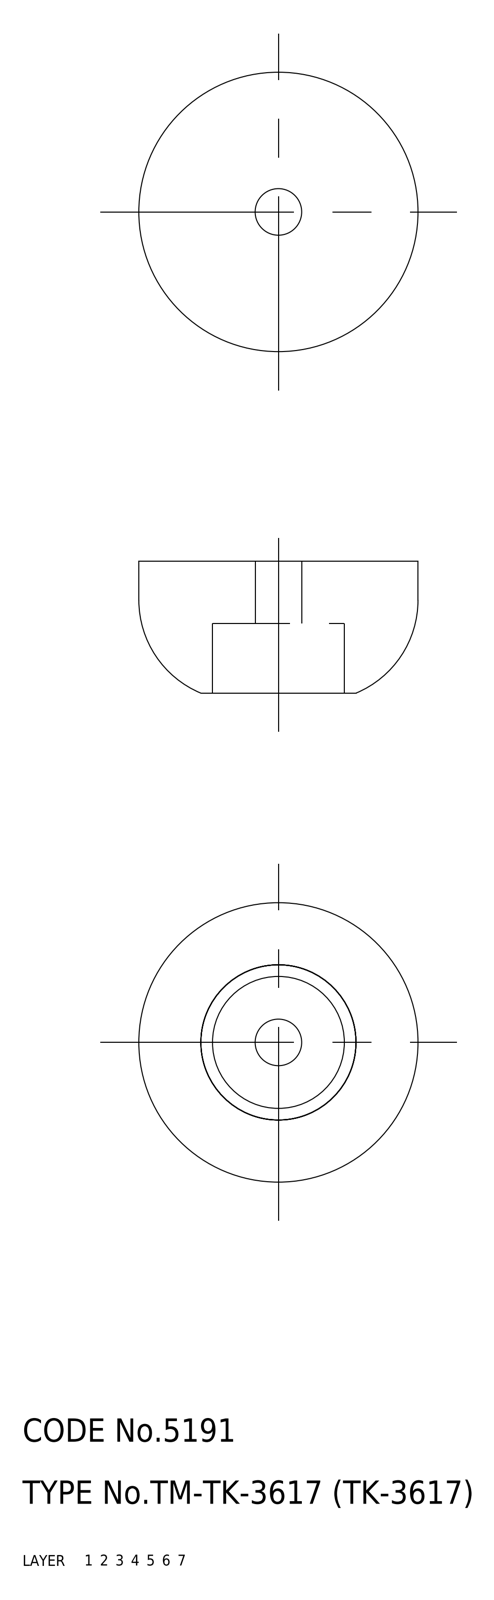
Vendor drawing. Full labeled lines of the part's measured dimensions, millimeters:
Part name (STEP PRODUCT): washer; rubber foot; TK_3617_9856_36
STEP written by: CADfix (AUTOMOTIVE_DESIGN)
Units: millimetres
Bodies: 2 solids, 20 faces (0 planar, 0 cylindrical, 20 other)
Overall size (bounding box): 36 × 36 × 17
Volume: 12 395 mm³ · Surface area: 4 555 mm²
